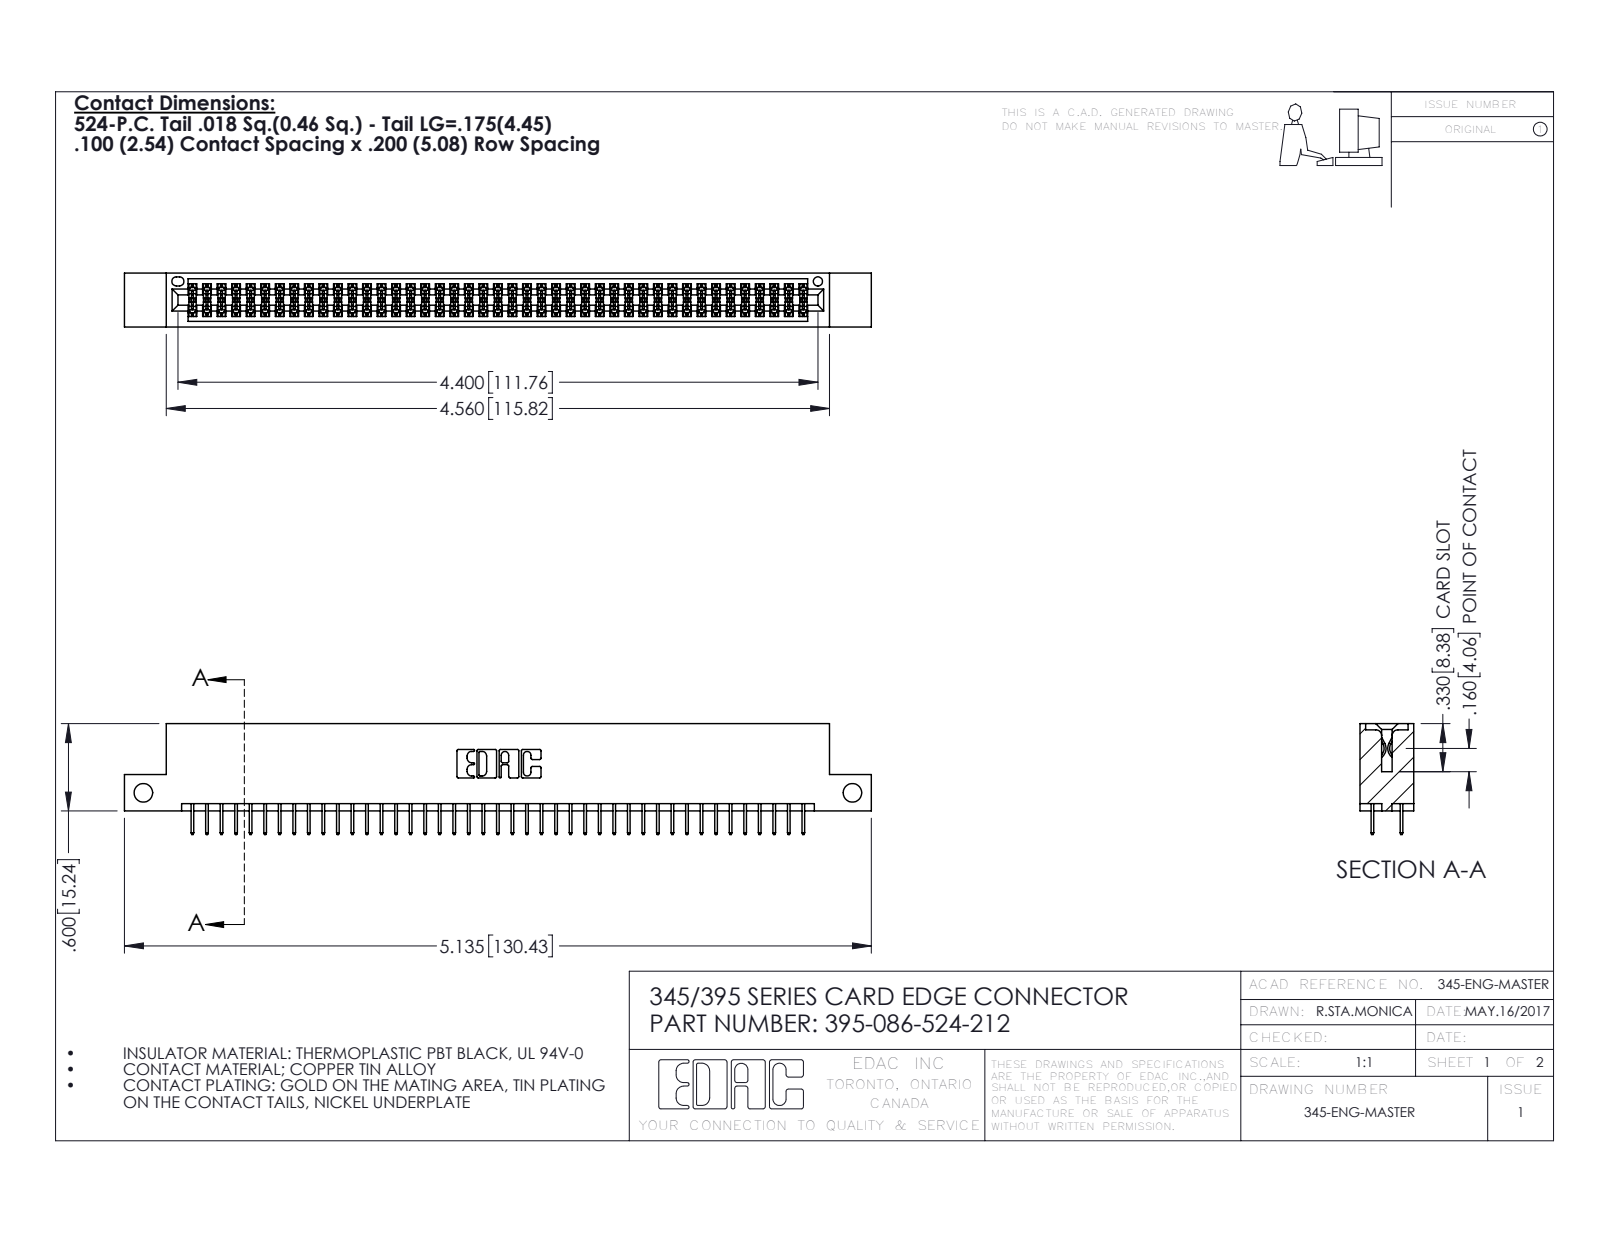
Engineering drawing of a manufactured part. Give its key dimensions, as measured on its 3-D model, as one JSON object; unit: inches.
{"part_name": "345-292-001_345-293-124; 395-086-524-212; 345 Part_Flush Mounting Lugs - Side Mount", "step_written_by": "SolidWorks 2016 (CONFIG_CONTROL_DESIGN)", "units": "inches", "bodies": {"solids": 87, "faces": 4770, "planar": 3434, "cylindrical": 1336, "other": 0}, "overall_size": [5.135, 0.762, 0.37], "volume_in3": 0.76, "surface_area_in2": 27.84, "round_holes": [[0.128, 2], [0.064, 1]], "partial_cylinders_radius": [[0.006, 129], [0.01, 22], [0.007, 6], [0.031, 6], [0.026, 3], [0.014, 2], [0.019, 2], [0.022, 2]], "face_to_face_distances": [0.298, 0.072, 0.2, 0.37, 0.098, 0.272, 0.025, 0.225, 0.072, 0.175], "hole_center_spacings": [4.875]}
